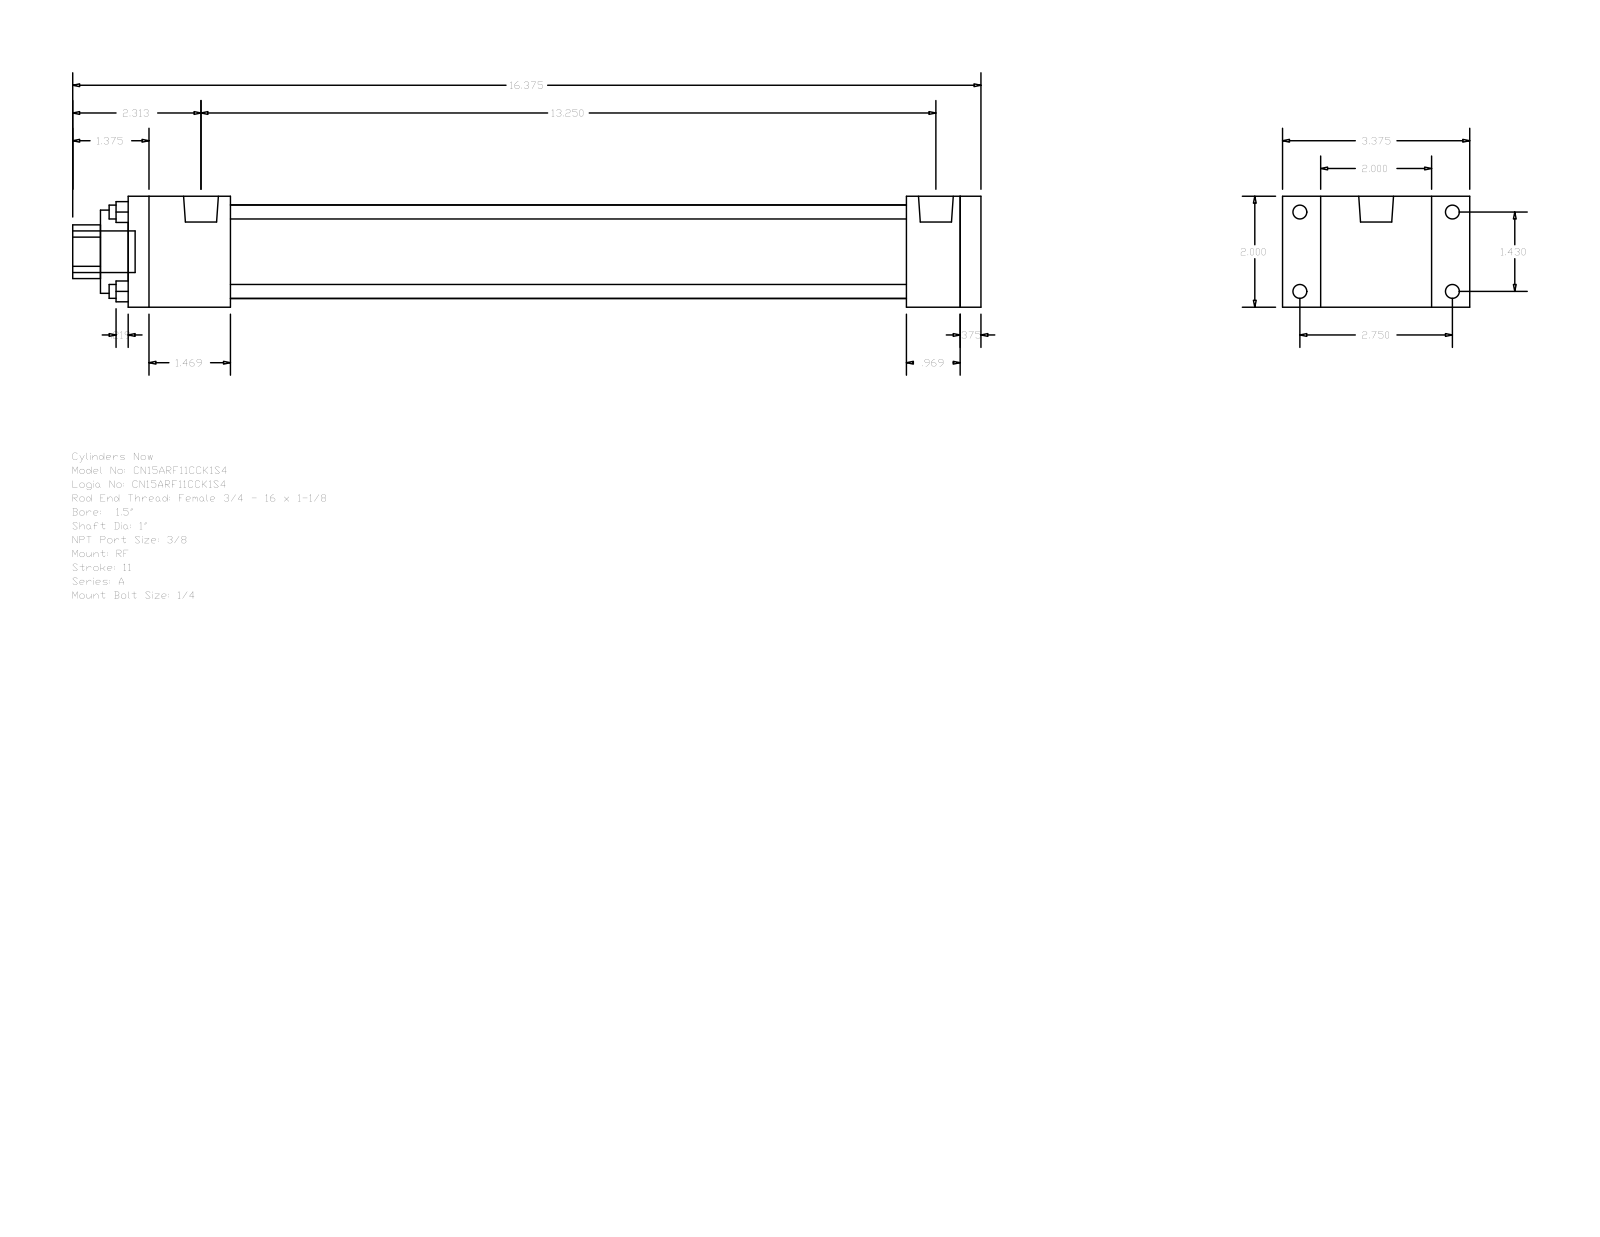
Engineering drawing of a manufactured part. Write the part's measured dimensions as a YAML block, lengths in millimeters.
part_name: "A_RF__0150_1"
step_written_by: "GSSL Pune (CONFIG_CONTROL_DESIGN)"
units: millimeters
bodies: {solids: 0, faces: 92, planar: 64, cylindrical: 28, other: 0}
overall_size: [415.93, 85.72, 50.8]
round_holes:
  - {diameter: 6.35, count: 4}
  - {diameter: 25.4, count: 1}
  - {diameter: 38.1, count: 1}
  - {diameter: 42.93, count: 1}
round_bosses_or_shafts:
  - {diameter: 6.35, count: 4}
  - {diameter: 5.56, count: 4}
  - {diameter: 15.93, count: 2}
  - {diameter: 19.05, count: 1}
partial_cylinders:
  - {radius: 12.29, count: 1}
face_to_face_distances: [50.8, 9.53, 381, 390.53, 356.39, 24.61, 34.14, 46.83, 309.56, 334.17]
hole_center_spacings: [25.68, 36.32, 51.36]
